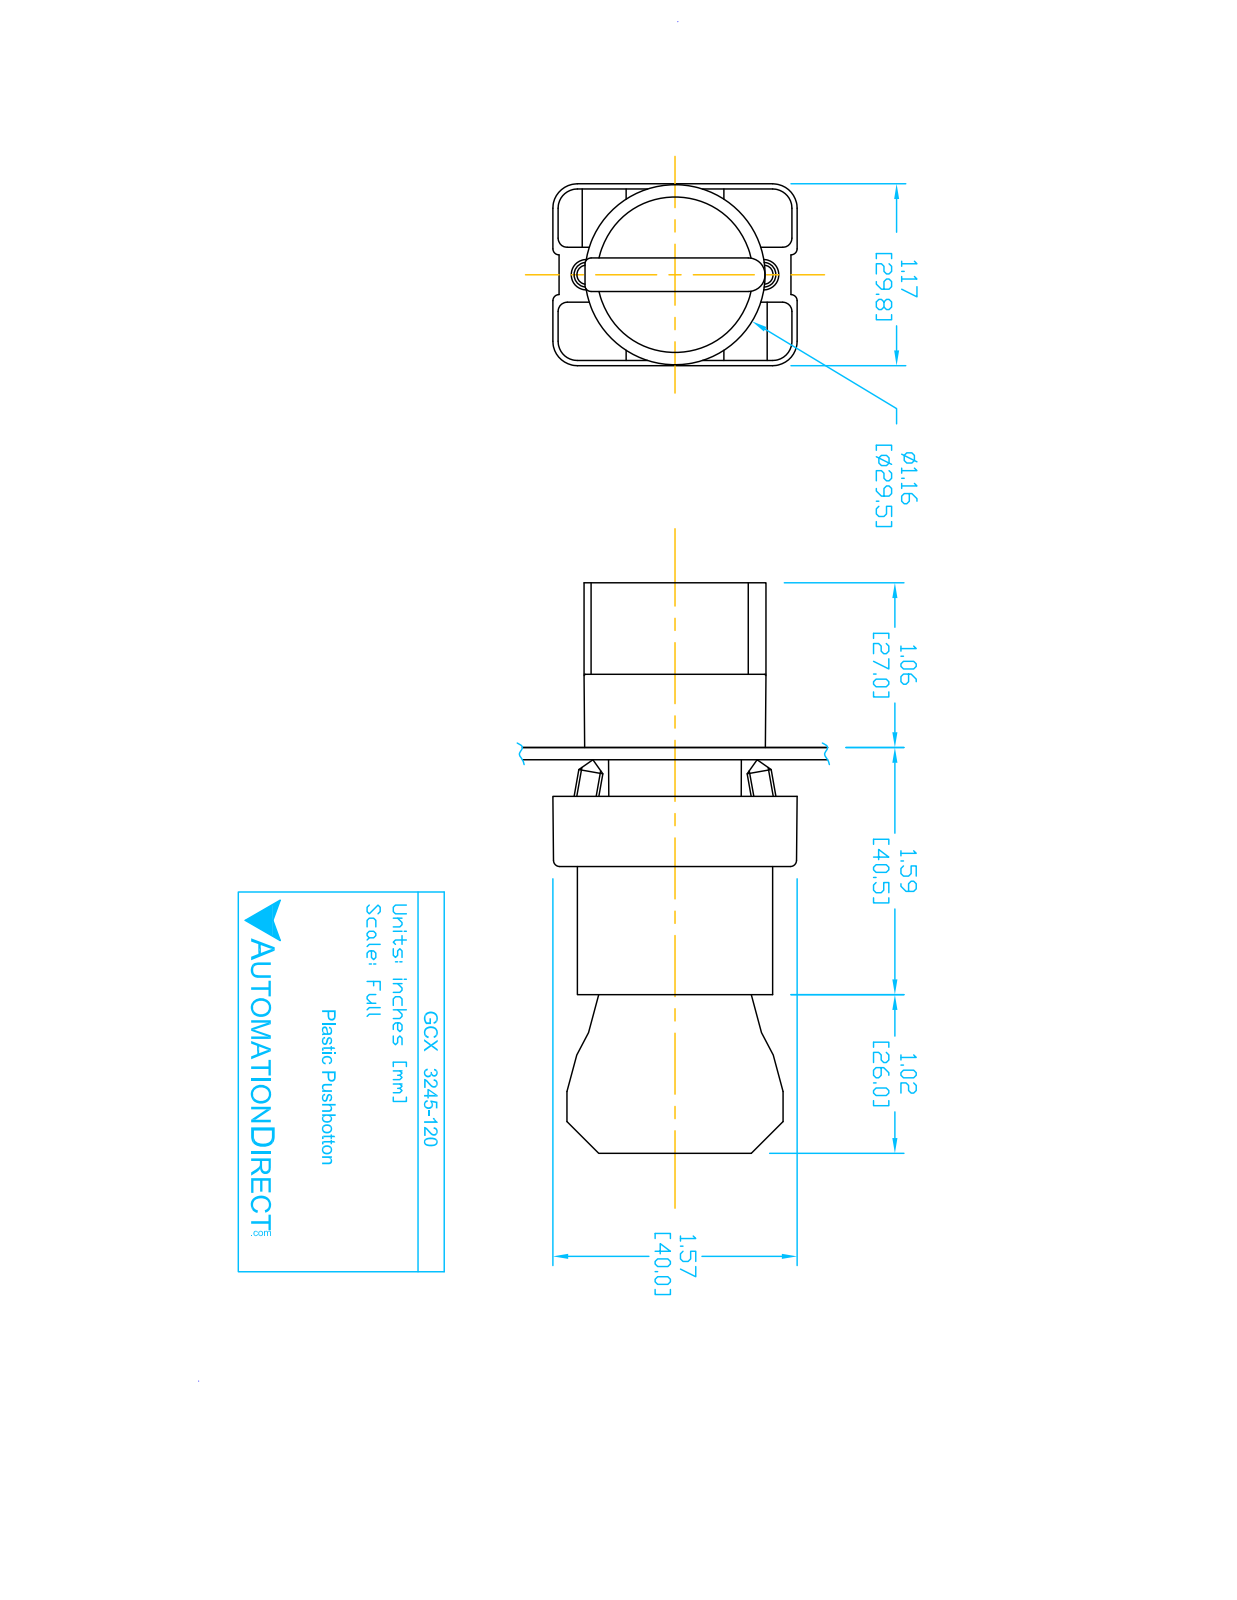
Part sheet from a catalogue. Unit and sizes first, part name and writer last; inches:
Units: inches
Overall size (bounding box): 3.653 × 1.581 × 1.177
Round holes (diameter × count): ⌀0.079 ×2, ⌀0.124 ×2, ⌀0.13 ×2, ⌀0.087 ×1, ⌀0.197 ×1, ⌀0.469 ×1, ⌀0.878 ×1, ⌀0.888 ×1, ⌀1.024 ×1
Round bosses / shafts (diameter × count): ⌀0.157 ×4, ⌀1.175 ×1, ⌀1.004 ×1, ⌀0.945 ×1, ⌀0.856 ×1, ⌀0.78 ×1, ⌀0.504 ×1
Partial cylindrical surfaces — rounded edges, fillets, slot ends (radius × count): R0.059 ×24, R0.041 ×12, R0.124 ×12, R0.157 ×12, R0.039 ×9, R0.128 ×2, R0.02 ×1, R0.063 ×1
Main face-to-face distances: 0.827, 2.02, 1.193, 0.579, 1.244, 1.171, 0.472, 0.469, 0.031, 0.033
Hole centre spacings: 0.236, 0.544, 0.472, 0.49
Volume: 2.799 in³ · Surface area: 39 in²
Bodies: 8 solids, 445 faces (263 planar, 151 cylindrical, 31 other)
Part name (STEP PRODUCT): GCX3245 OPERATOR; GCX3245-120; ECX3029-2; ECX1050 (+1 more)
STEP written by: SolidWorks 2016 (AUTOMOTIVE_DESIGN)
